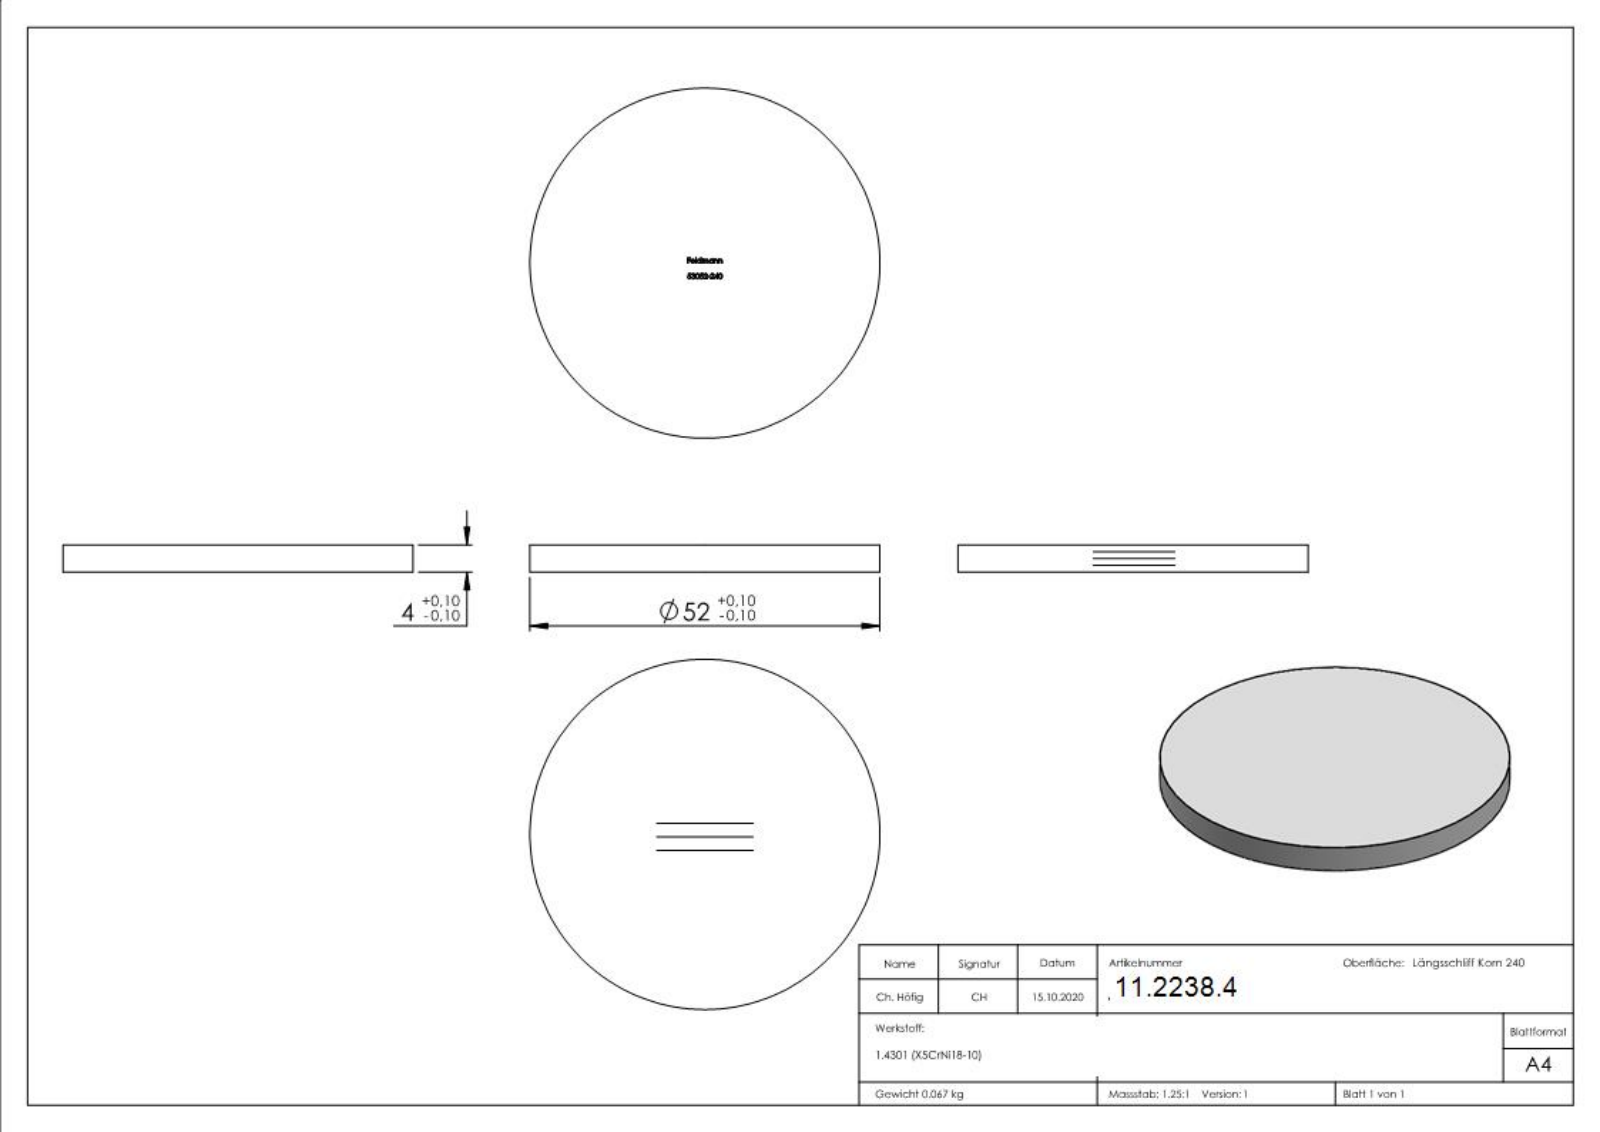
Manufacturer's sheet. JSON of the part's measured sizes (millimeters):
{"part_name": "53052-240", "step_written_by": "SolidWorks 2018 (CONFIG_CONTROL_DESIGN)", "units": "millimeters", "bodies": {"solids": 1, "faces": 233, "planar": 123, "cylindrical": 2, "other": 108}, "overall_size": [52, 52, 4], "volume_mm3": 8495, "surface_area_mm2": 4907, "round_bosses_or_shafts": [[52, 1]], "face_to_face_distances": [4, 3.9, 0.71, 1.78, 2.45, 0.83, 0.79, 2.41, 0.99, 0.4]}
